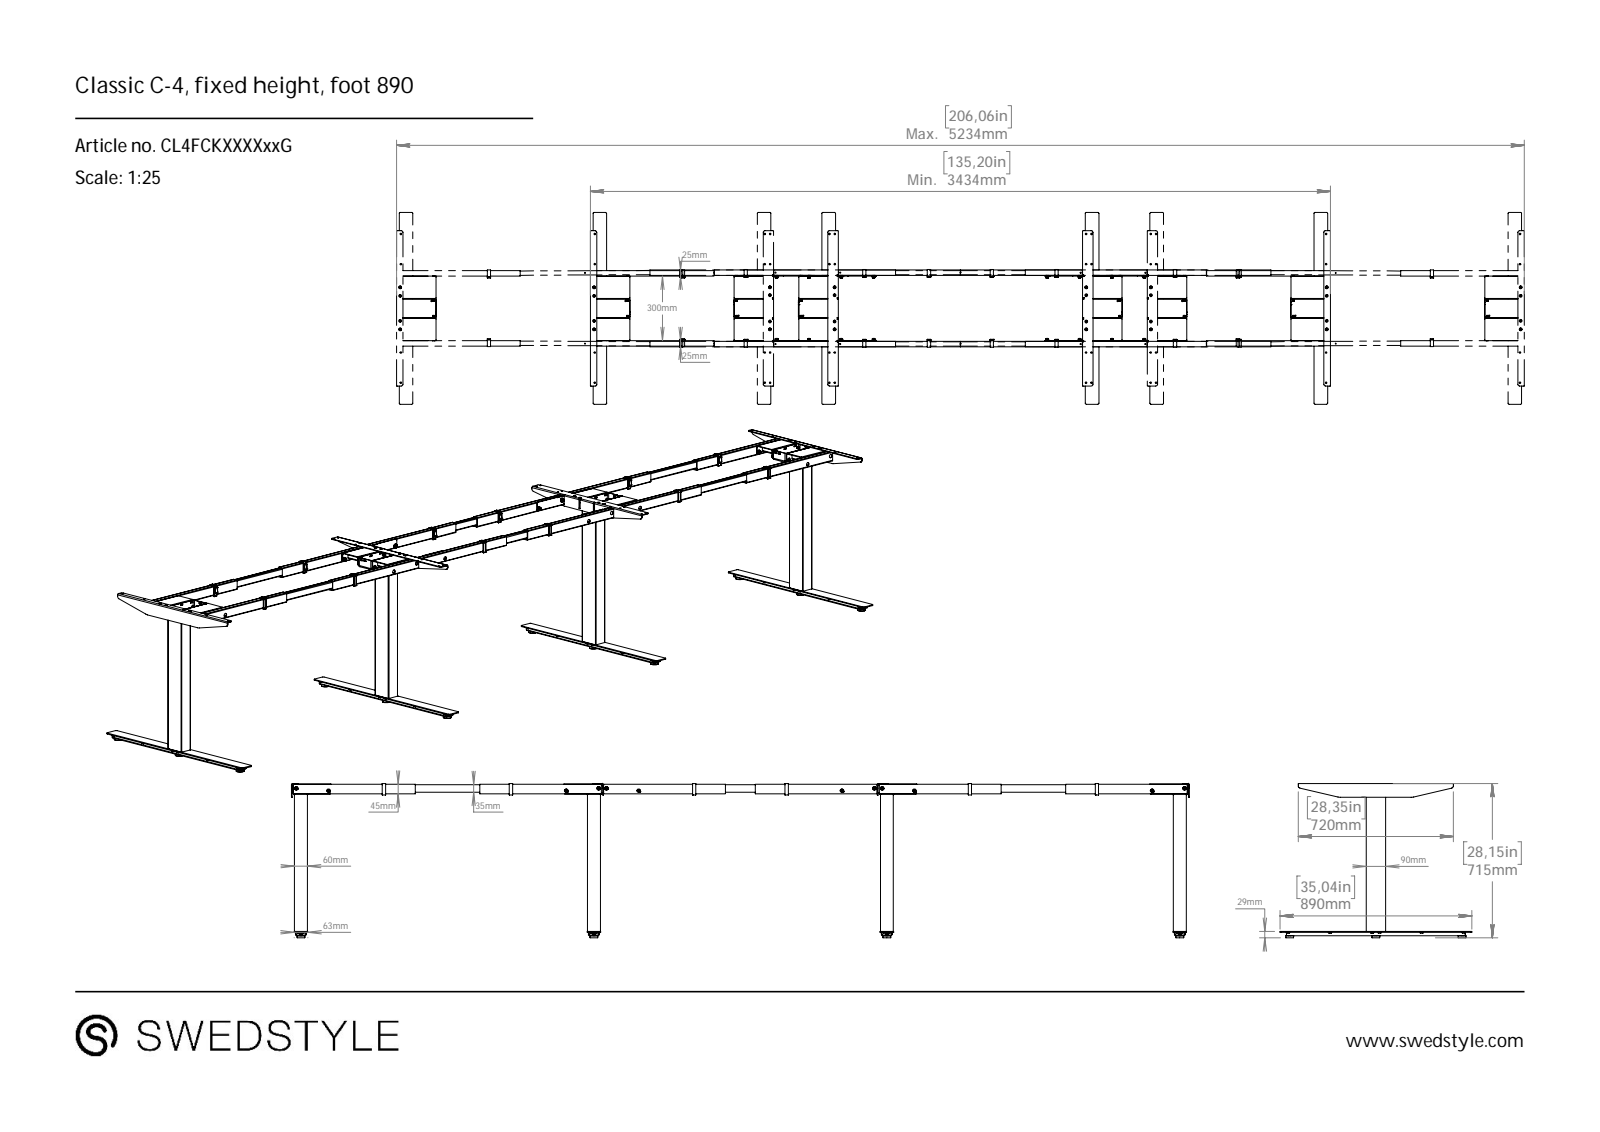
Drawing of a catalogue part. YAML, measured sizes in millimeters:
part_name: "Classic C-4, fixed height, foot 890_CL4FCKXXXXxxG"
step_written_by: "SolidWorks 2021 (CONFIG_CONTROL_DESIGN)"
units: millimeters
bodies: {solids: 0, faces: 1901, planar: 870, cylindrical: 679, other: 352}
overall_size: [3800, 890, 715.6]
round_holes:
  - {diameter: 7, count: 24}
  - {diameter: 16, count: 20}
  - {diameter: 4.2, count: 6}
  - {diameter: 5, count: 4}
  - {diameter: 7.5, count: 4}
  - {diameter: 5.4, count: 2}
  - {diameter: 6, count: 2}
round_bosses_or_shafts:
  - {diameter: 11.65, count: 4}
  - {diameter: 9.8, count: 2}
  - {diameter: 8, count: 2}
partial_cylinders:
  - {radius: 2.5, count: 127}
  - {radius: 5, count: 28}
  - {radius: 3.5, count: 24}
  - {radius: 4.5, count: 22}
  - {radius: 7, count: 18}
  - {radius: 0.5, count: 16}
  - {radius: 3, count: 16}
  - {radius: 1, count: 10}
face_to_face_distances: [3, 2, 23, 20, 328, 2.5, 2474.67, 0.5, 331, 25]
hole_center_spacings: [140, 550, 25, 34, 142.21, 550.57, 646.94, 655.58]
